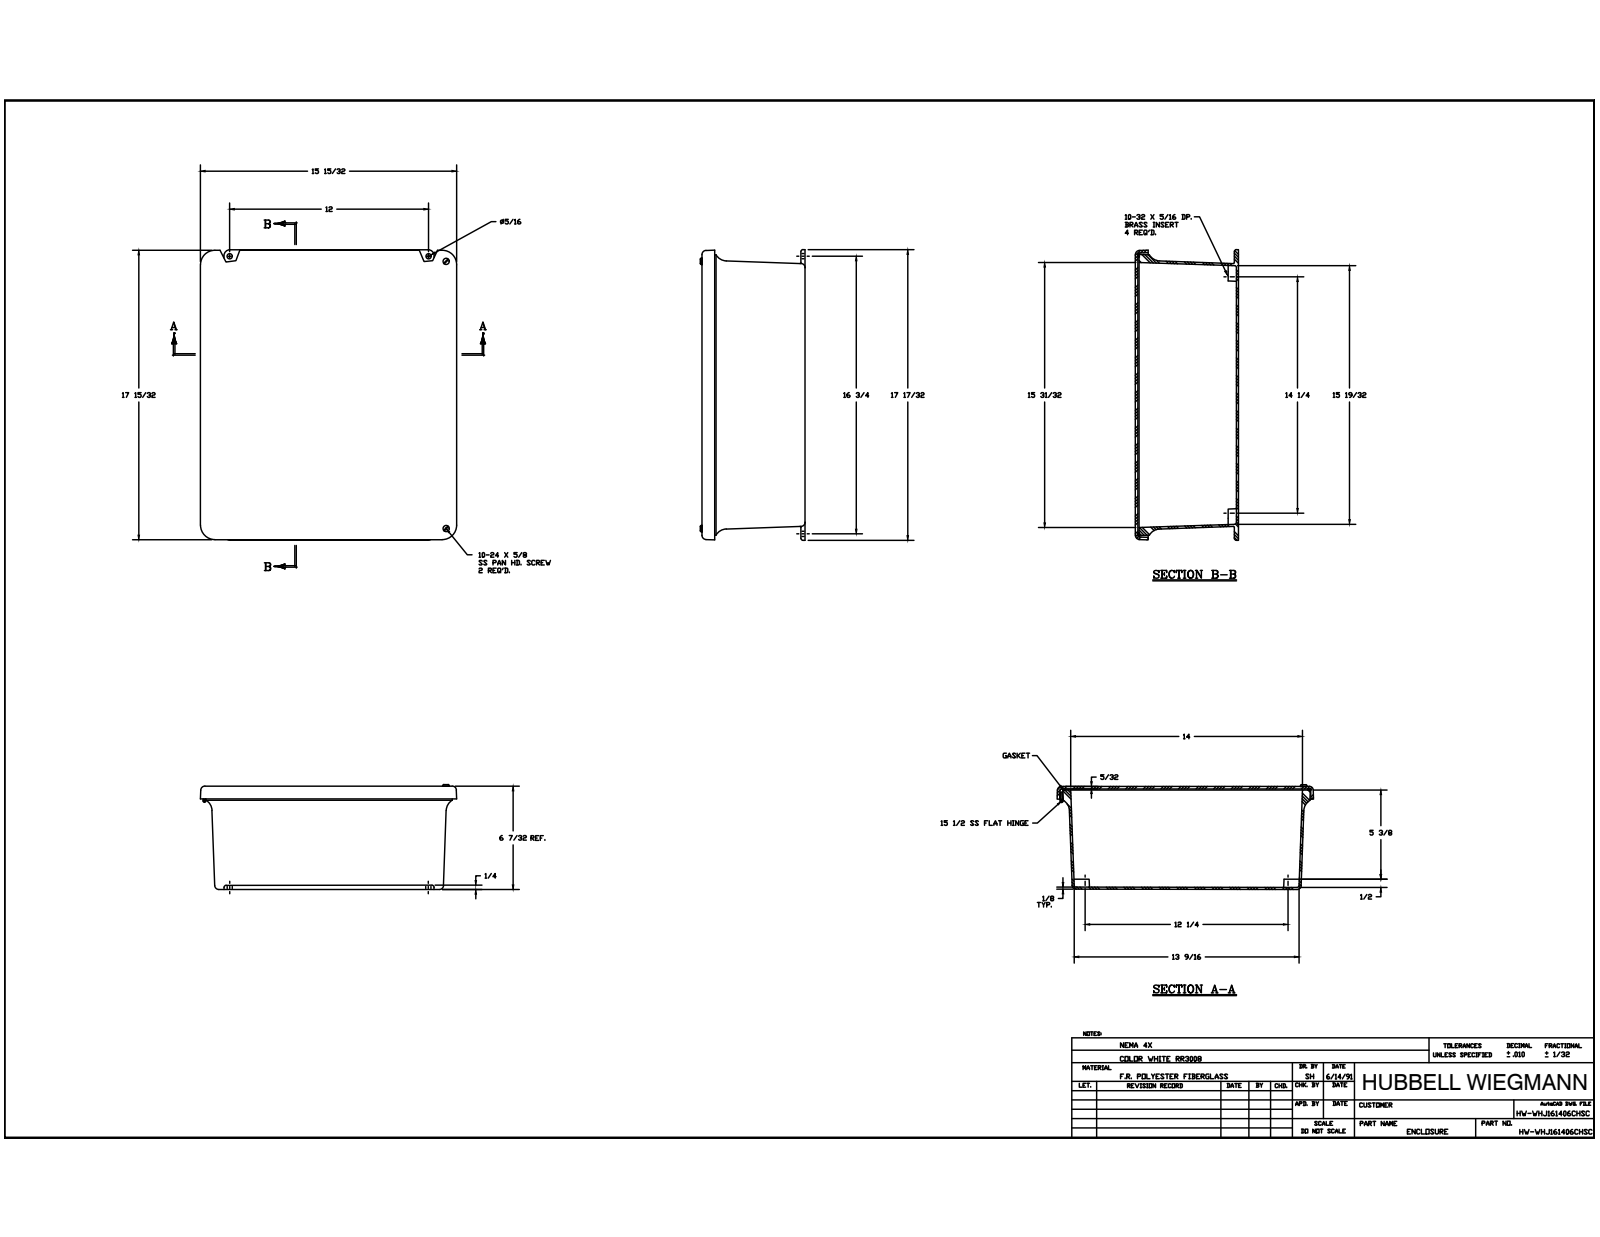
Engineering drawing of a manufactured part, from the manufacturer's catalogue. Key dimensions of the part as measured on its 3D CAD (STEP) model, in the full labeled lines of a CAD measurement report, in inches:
Part name (STEP PRODUCT): J1614HW_1; RMINS45821P_39; RMINS45821P_40; RMINS45821P_41 (+8 more)
STEP written by: Autodesk Inventor 2014 (AUTOMOTIVE_DESIGN)
Units: inches
Bodies: 24 solids, 898 faces (341 planar, 350 cylindrical, 207 other)
Overall size (bounding box): 17.531 × 15.491 × 6.353
Volume: 143.6 in³ · Surface area: 1 938 in²
Round holes (diameter × count): ⌀0.131 ×10, ⌀0.14 ×10, ⌀0.152 ×8, ⌀0.156 ×4, ⌀0.218 ×4, ⌀0.145 ×2, ⌀0.085 ×1
Round bosses / shafts (diameter × count): ⌀0.25 ×10, ⌀0.125 ×10, ⌀0.27 ×6, ⌀0.19 ×2, ⌀0.156 ×2, ⌀0.155 ×1
Partial cylindrical surfaces — rounded edges, fillets, slot ends (radius × count): R0.031 ×20, R0.125 ×12, R0.25 ×12, R0.2 ×5, R0.375 ×4, R0.75 ×4, R0.063 ×2
Main face-to-face distances: 0.125, 0.152, 6.07, 6.222, 5.944, 6.096, 0.125, 6, 5.875, 0.07
Hole centre spacings: 3.75, 7.5, 11.25, 0.25, 3.5, 1.321, 7.25, 13.22
